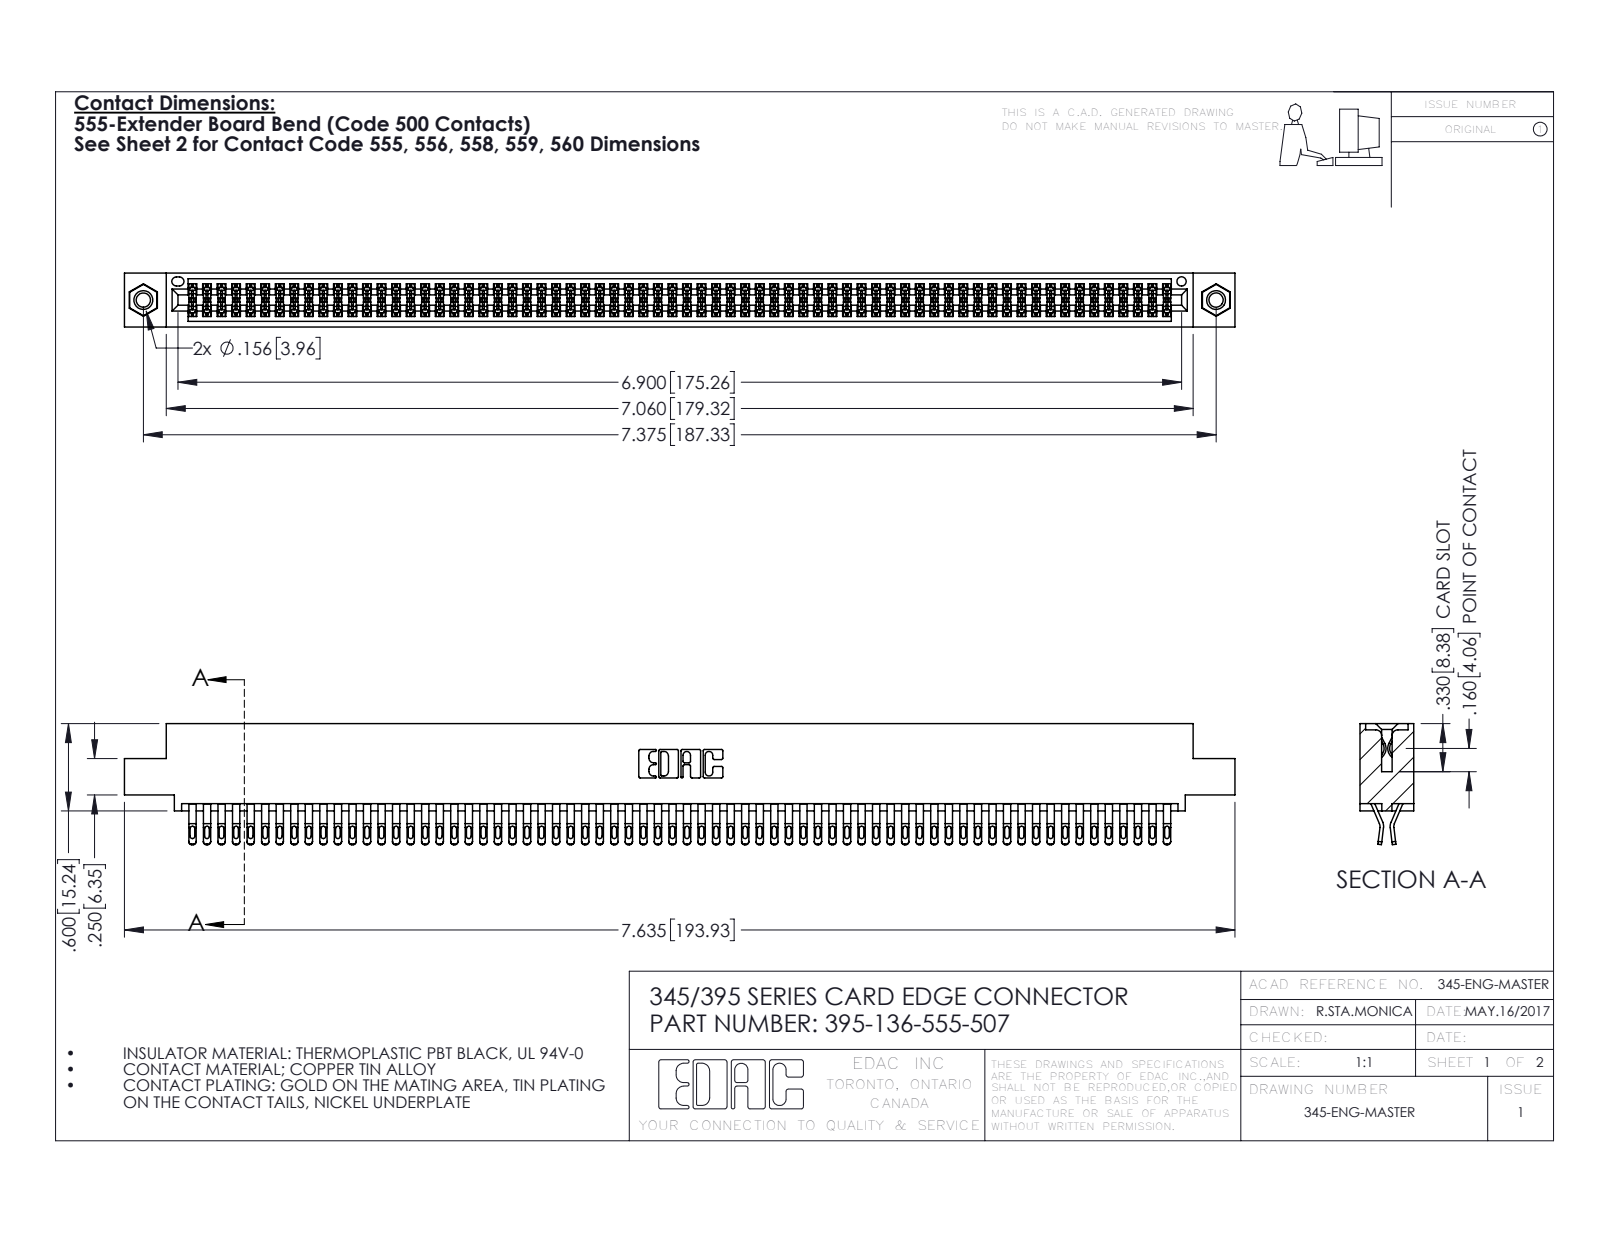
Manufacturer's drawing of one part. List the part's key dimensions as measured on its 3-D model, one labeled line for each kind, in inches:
Part name (STEP PRODUCT): 395-136-555-507; 345-292-001_555 Tail; 345 Part_0.110 Offset - 0.156 Dia-TI; 345-250-001_345-250-005-103
STEP written by: SolidWorks 2016 (CONFIG_CONTROL_DESIGN)
Units: inches
Bodies: 139 solids, 7806 faces (4332 planar, 3458 cylindrical, 16 other)
Overall size (bounding box): 7.635 × 0.832 × 0.37
Volume: 1.183 in³ · Surface area: 47.51 in²
Round holes (diameter × count): ⌀0.098 ×2, ⌀0.125 ×2, ⌀0.156 ×2, ⌀0.064 ×1
Round bosses / shafts (diameter × count): ⌀0.155 ×2
Partial cylindrical surfaces — rounded edges, fillets, slot ends (radius × count): R0.016 ×340, R0.02 ×272, R0.006 ×204, R0.01 ×22, R0.007 ×6, R0.031 ×6, R0.026 ×3, R0.01 ×2
Main face-to-face distances: 0.072, 0.298, 0.025, 0.37, 0.2, 0.098, 0.272, 0.225, 0.175, 0.149
Hole centre spacings: 0.27, 7.139, 7.375
